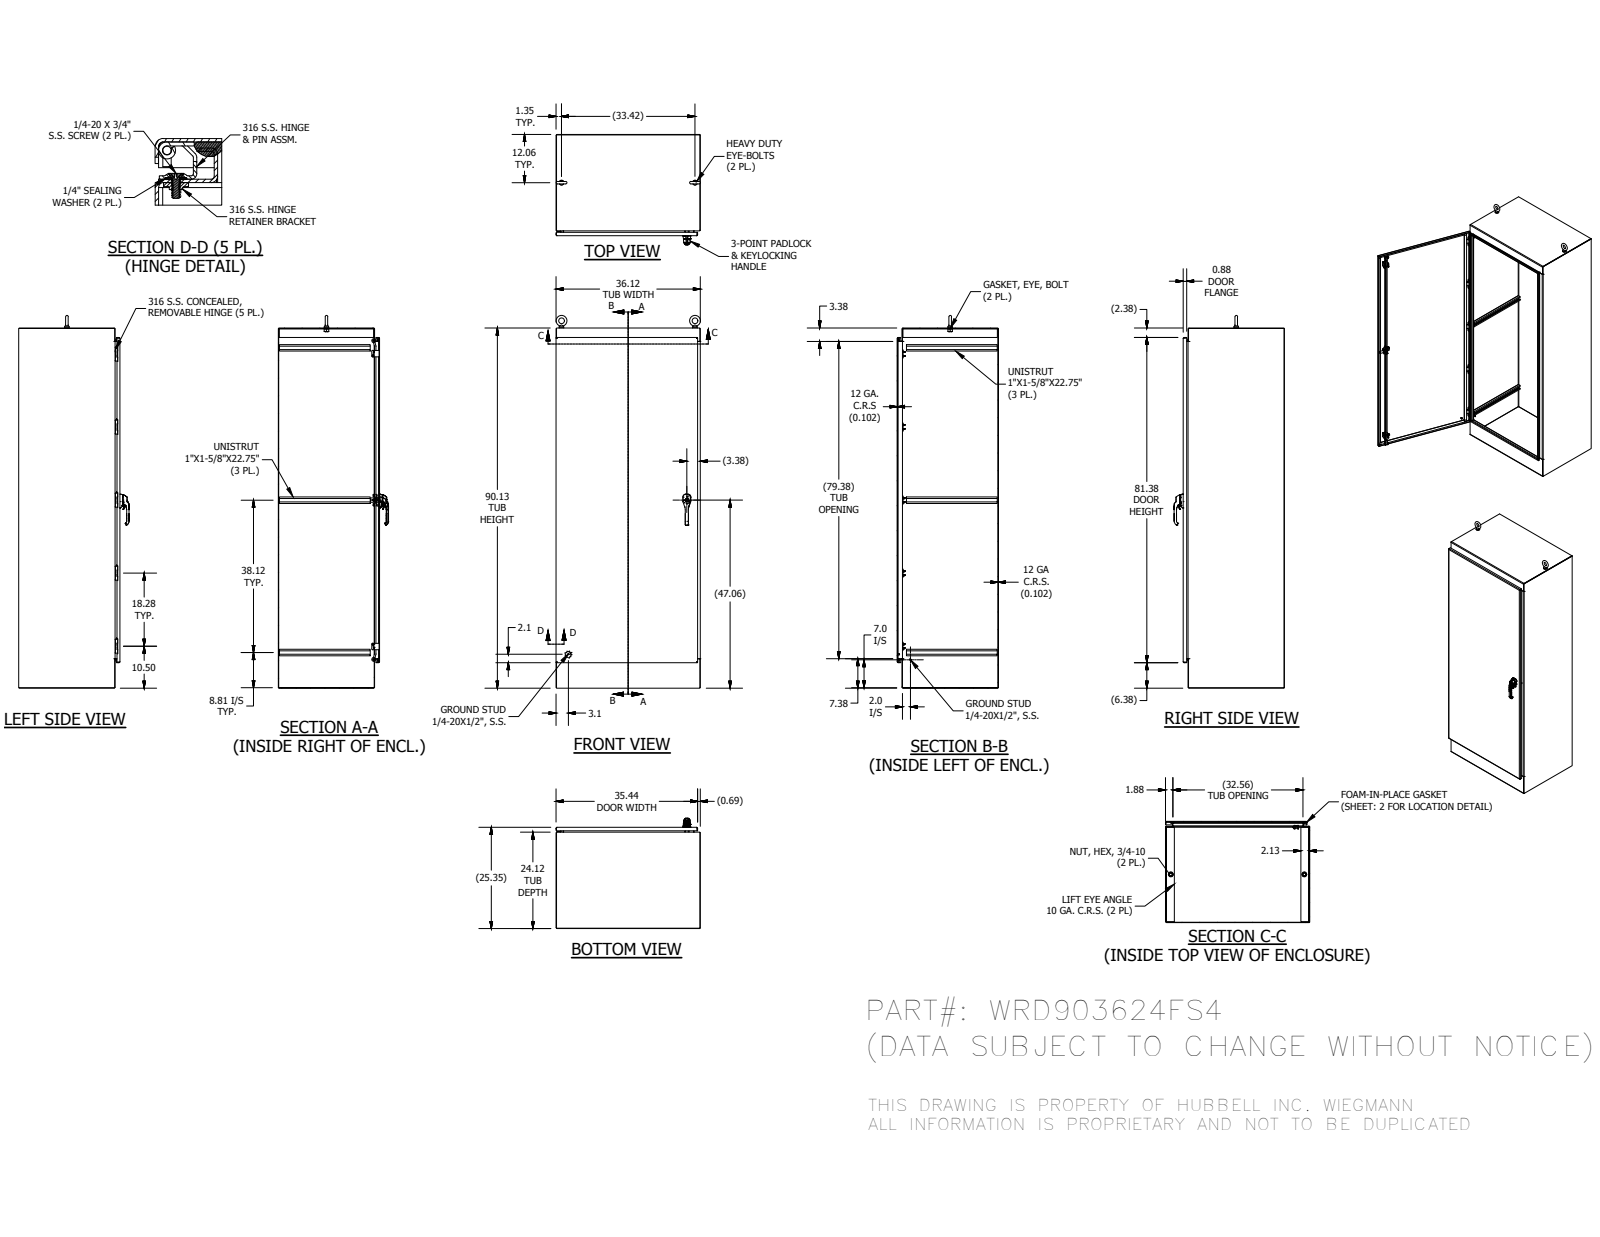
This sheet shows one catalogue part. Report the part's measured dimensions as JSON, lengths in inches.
{"part_name": "WRD903624FS4BLS; WRD3624FS4TOP; WRD3624FS4BTM; WRD9036FS4DR (+8 more)", "step_written_by": "Autodesk Inventor 2016 (AUTOMOTIVE_DESIGN)", "units": "inches", "bodies": {"solids": 94, "faces": 3829, "planar": 1580, "cylindrical": 1269, "other": 980}, "overall_size": [93.248, 36.127, 27.616], "volume_in3": 1529, "surface_area_in2": 29310, "round_holes": [[0.23, 10], [0.281, 10], [0.65, 10], [0.276, 8], [0.2, 4], [0.213, 3], [0.236, 3], [0.28, 3], [0.241, 2], [0.25, 2], [0.252, 2], [0.4, 2]], "round_bosses_or_shafts": [[0.25, 18], [0.625, 10], [0.404, 10], [0.182, 10], [1.25, 2], [1.12, 2], [1, 2], [0.75, 2]], "partial_cylinders_radius": [[0.02, 164], [0.012, 86], [0.063, 33], [0.01, 26], [0.125, 22], [0.019, 19], [0.079, 15], [0.05, 14]], "face_to_face_distances": [0.102, 25.245, 36.023, 25.143, 25.347, 35.921, 36.125, 90.023, 24.023, 1.222], "hole_center_spacings": [1, 0.492, 18.281, 18.281, 36.563, 54.844, 0.256, 0.886]}
